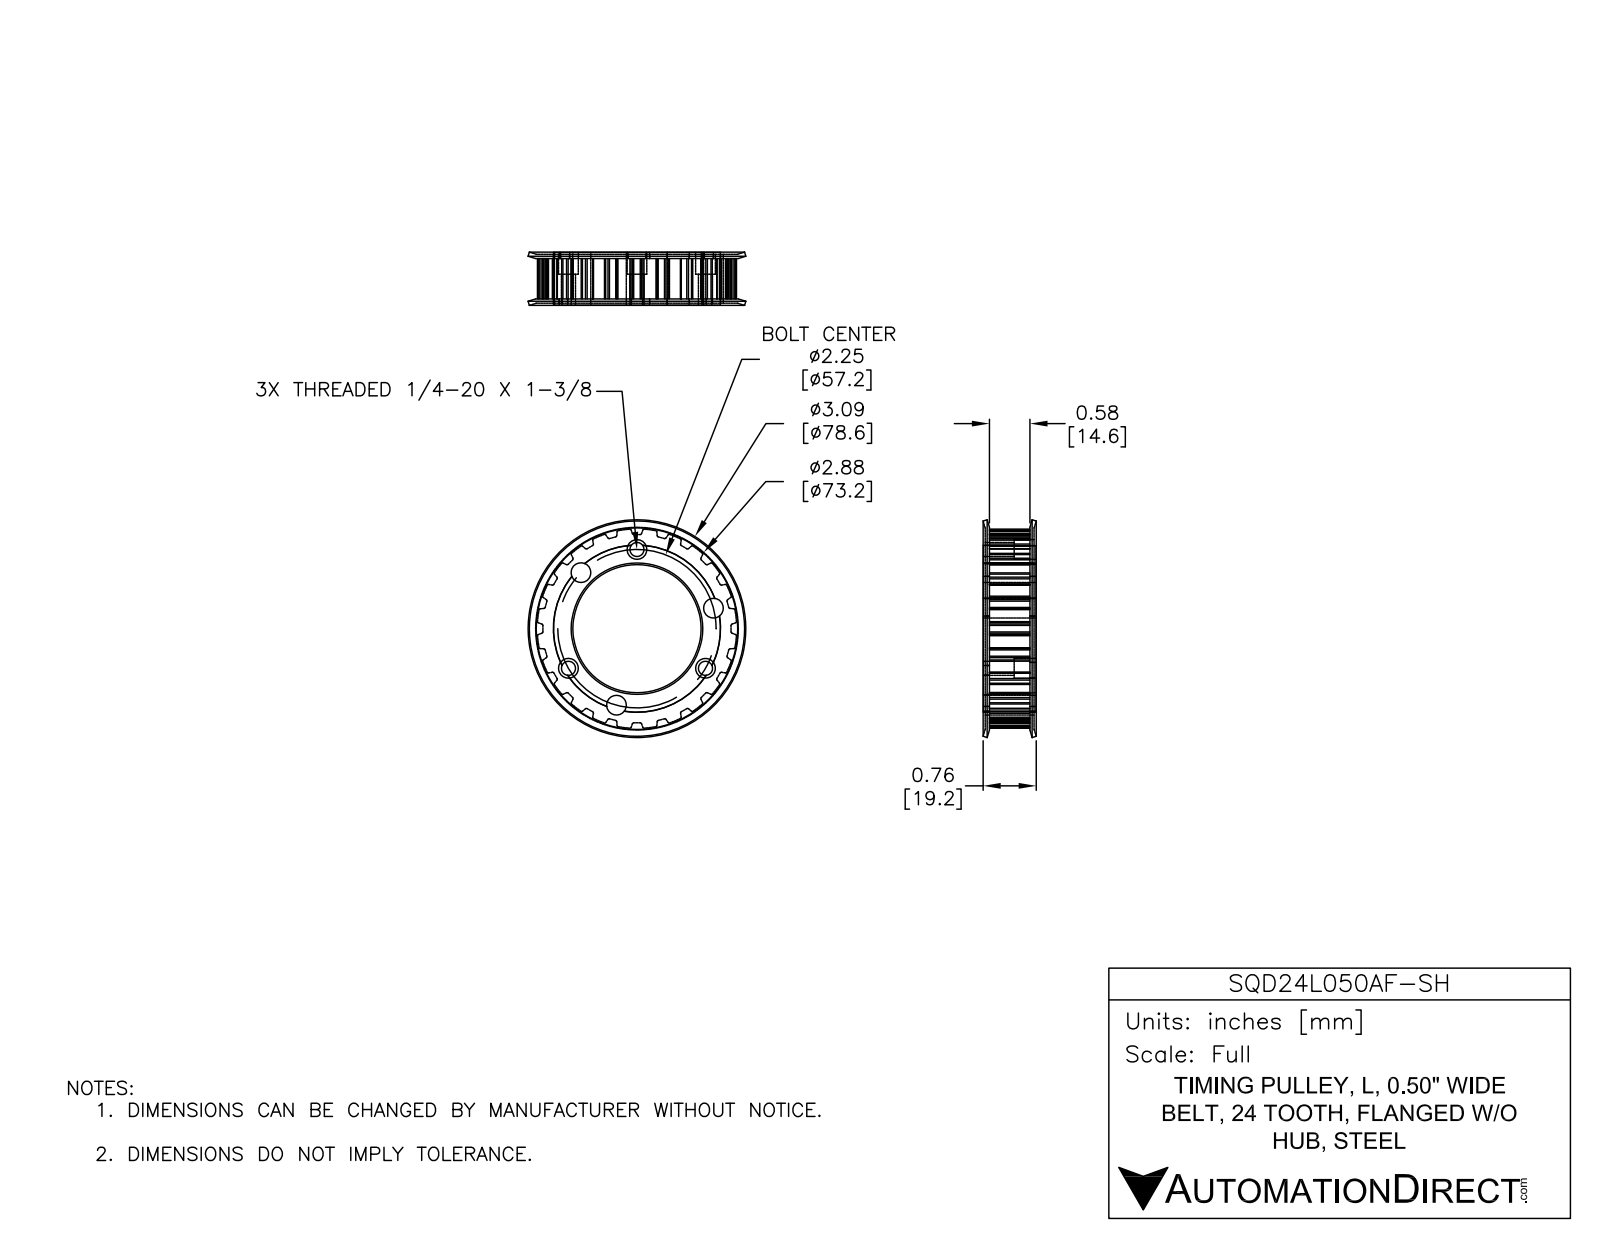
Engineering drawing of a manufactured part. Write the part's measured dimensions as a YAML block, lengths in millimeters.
part_name: "SQD24L050AF-SH"
step_written_by: "SolidWorks 2018 (AUTOMOTIVE_DESIGN)"
units: millimeters
bodies: {solids: 3, faces: 296, planar: 83, cylindrical: 197, other: 16}
overall_size: [78.6, 78.6, 19.2]
volume: 38720
surface_area: 22740
round_holes:
  - {diameter: 7.1, count: 6}
  - {diameter: 5.1, count: 3}
round_bosses_or_shafts:
  - {diameter: 60.2, count: 1}
partial_cylinders:
  - {radius: 0.4, count: 48}
  - {radius: 0.5, count: 48}
  - {radius: 3.6, count: 6}
  - {radius: 30.1, count: 1}
  - {radius: 30.2, count: 1}
  - {radius: 36, count: 1}
face_to_face_distances: [1.5, 16.1, 14.6, 0.7, 2.2, 16.8, 18.3, 17.7, 19.1, 20.4]
hole_center_spacings: [49.5, 21.9, 21.9, 34.8, 34.8, 34.8, 49.5, 49.5]
